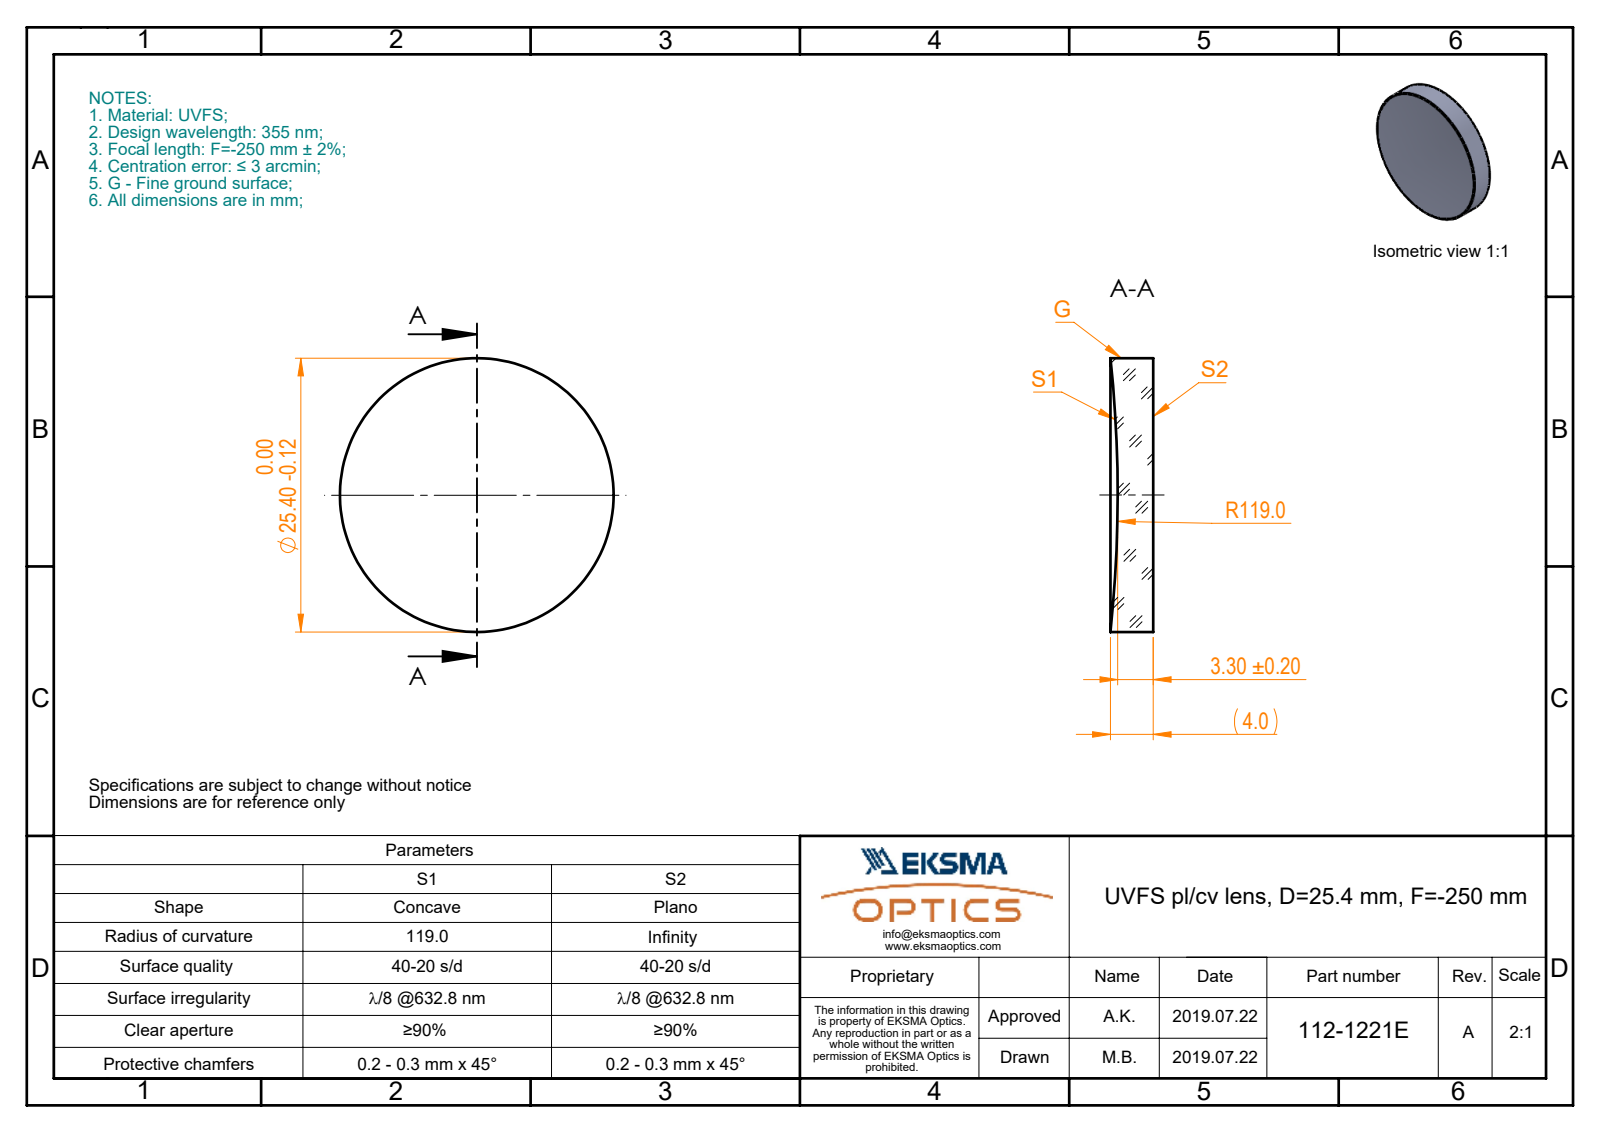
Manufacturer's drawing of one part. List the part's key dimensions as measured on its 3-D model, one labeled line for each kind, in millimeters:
Part name (STEP PRODUCT): 112-1221E UVFS pl-cv 25.4 F-250
STEP written by: SolidWorks 2017 (CONFIG_CONTROL_DESIGN)
Units: millimetres
Bodies: 1 solid, 5 faces (1 planar, 2 cylindrical, 2 other)
Overall size (bounding box): 25.4 × 25.4 × 3.98
Volume: 1 844 mm³ · Surface area: 1 332 mm²
Round bosses / shafts (diameter × count): ⌀25.4 ×1
